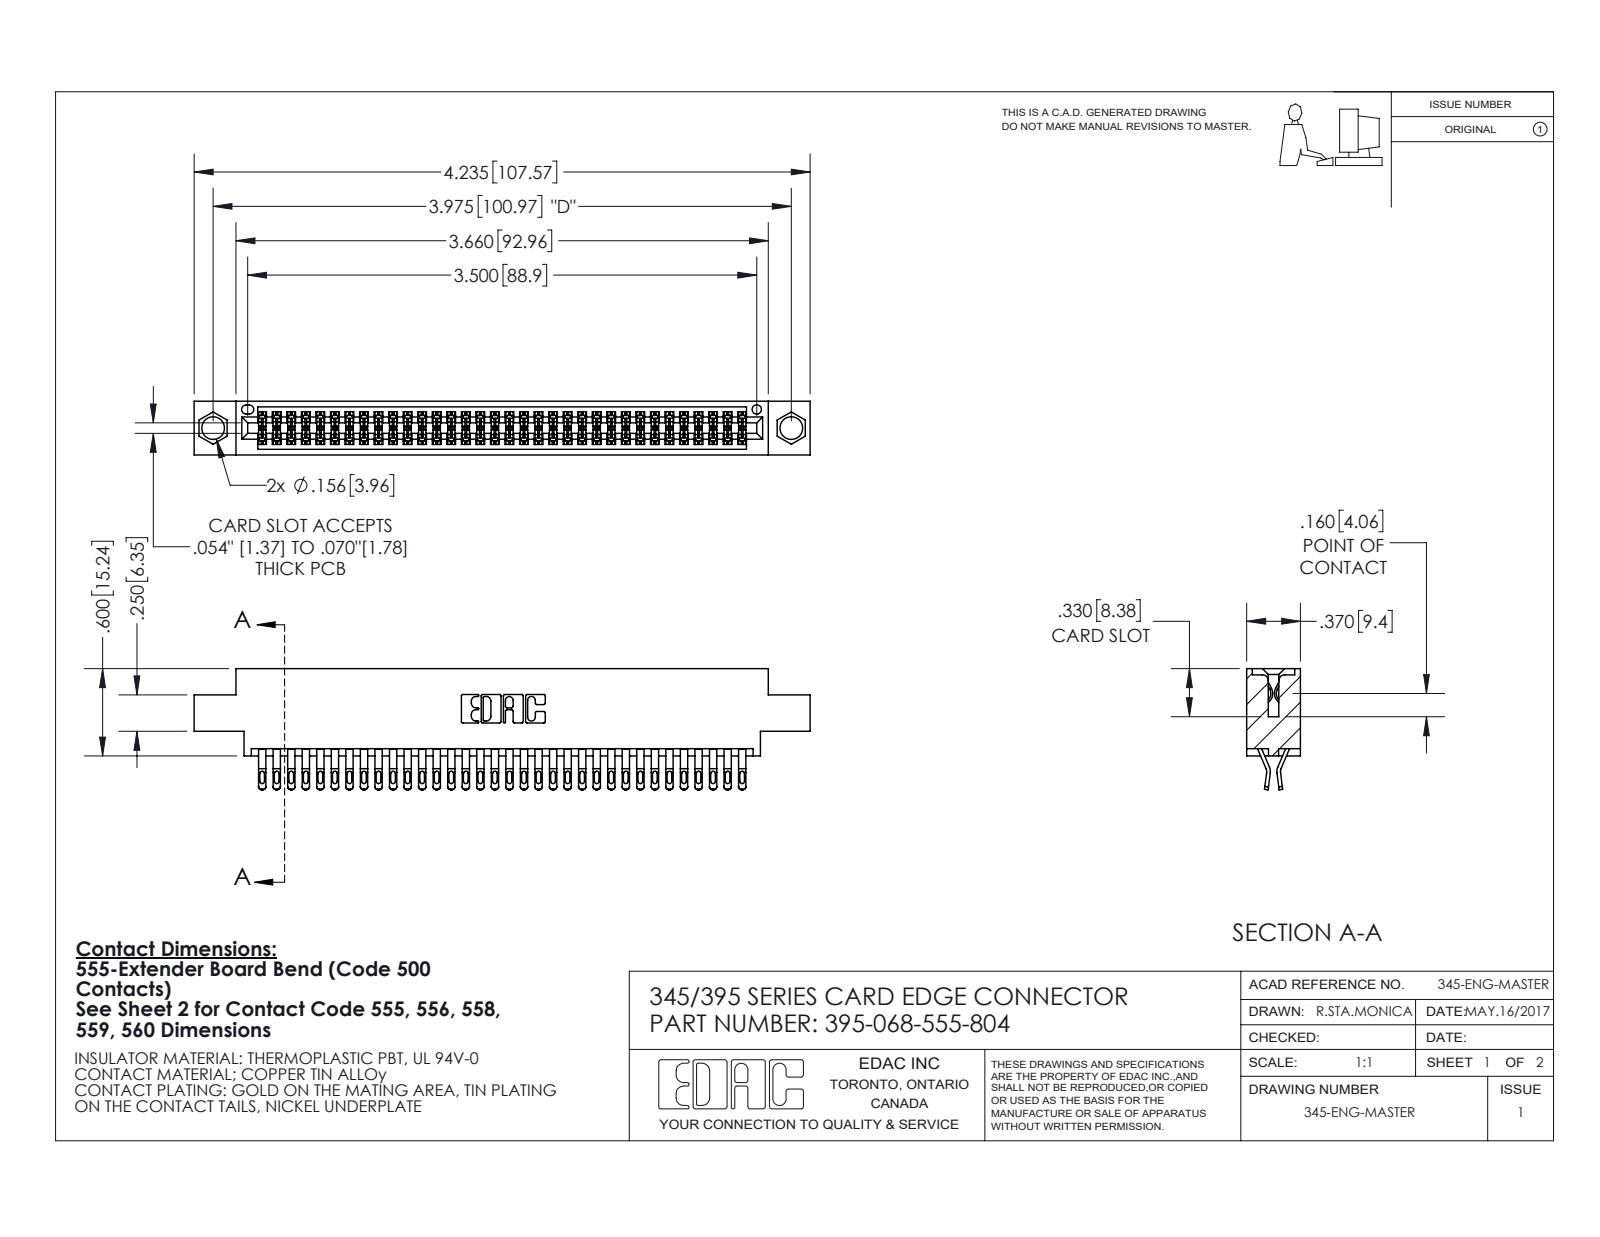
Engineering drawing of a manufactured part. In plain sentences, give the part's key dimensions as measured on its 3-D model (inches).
The part is named "395-068-555-804; 345-292-001_555 Tail; 345 Part_0.170 Offset - 0.156 Dia-TI". Its 3-D file was written by "SolidWorks 2020 (CONFIG_CONTROL_DESIGN)". It is 69 solids with 3952 faces: 2206 planar, 1746 cylindrical and 0 other. Overall it measures 4.235 by 0.832 by 0.37 inches. Its volume is 0.632 cubic inches and its surface area 24.54 square inches. Round holes: 2 of diameter 0.156, 1 of diameter 0.064. Partial cylindrical surfaces (rounded edges, fillets, slot ends): 170 of radius 0.016, 136 of radius 0.02, 102 of radius 0.006, 22 of radius 0.01, 6 of radius 0.007, 6 of radius 0.031, 3 of radius 0.026, 2 of radius 0.01. The main face-to-face distances are 0.298, 0.072, 0.37, 0.025, 0.2, 0.098, 0.272, 0.225, 0.175, 0.149. The hole center spacings are 0.27, 3.74, 3.975.
